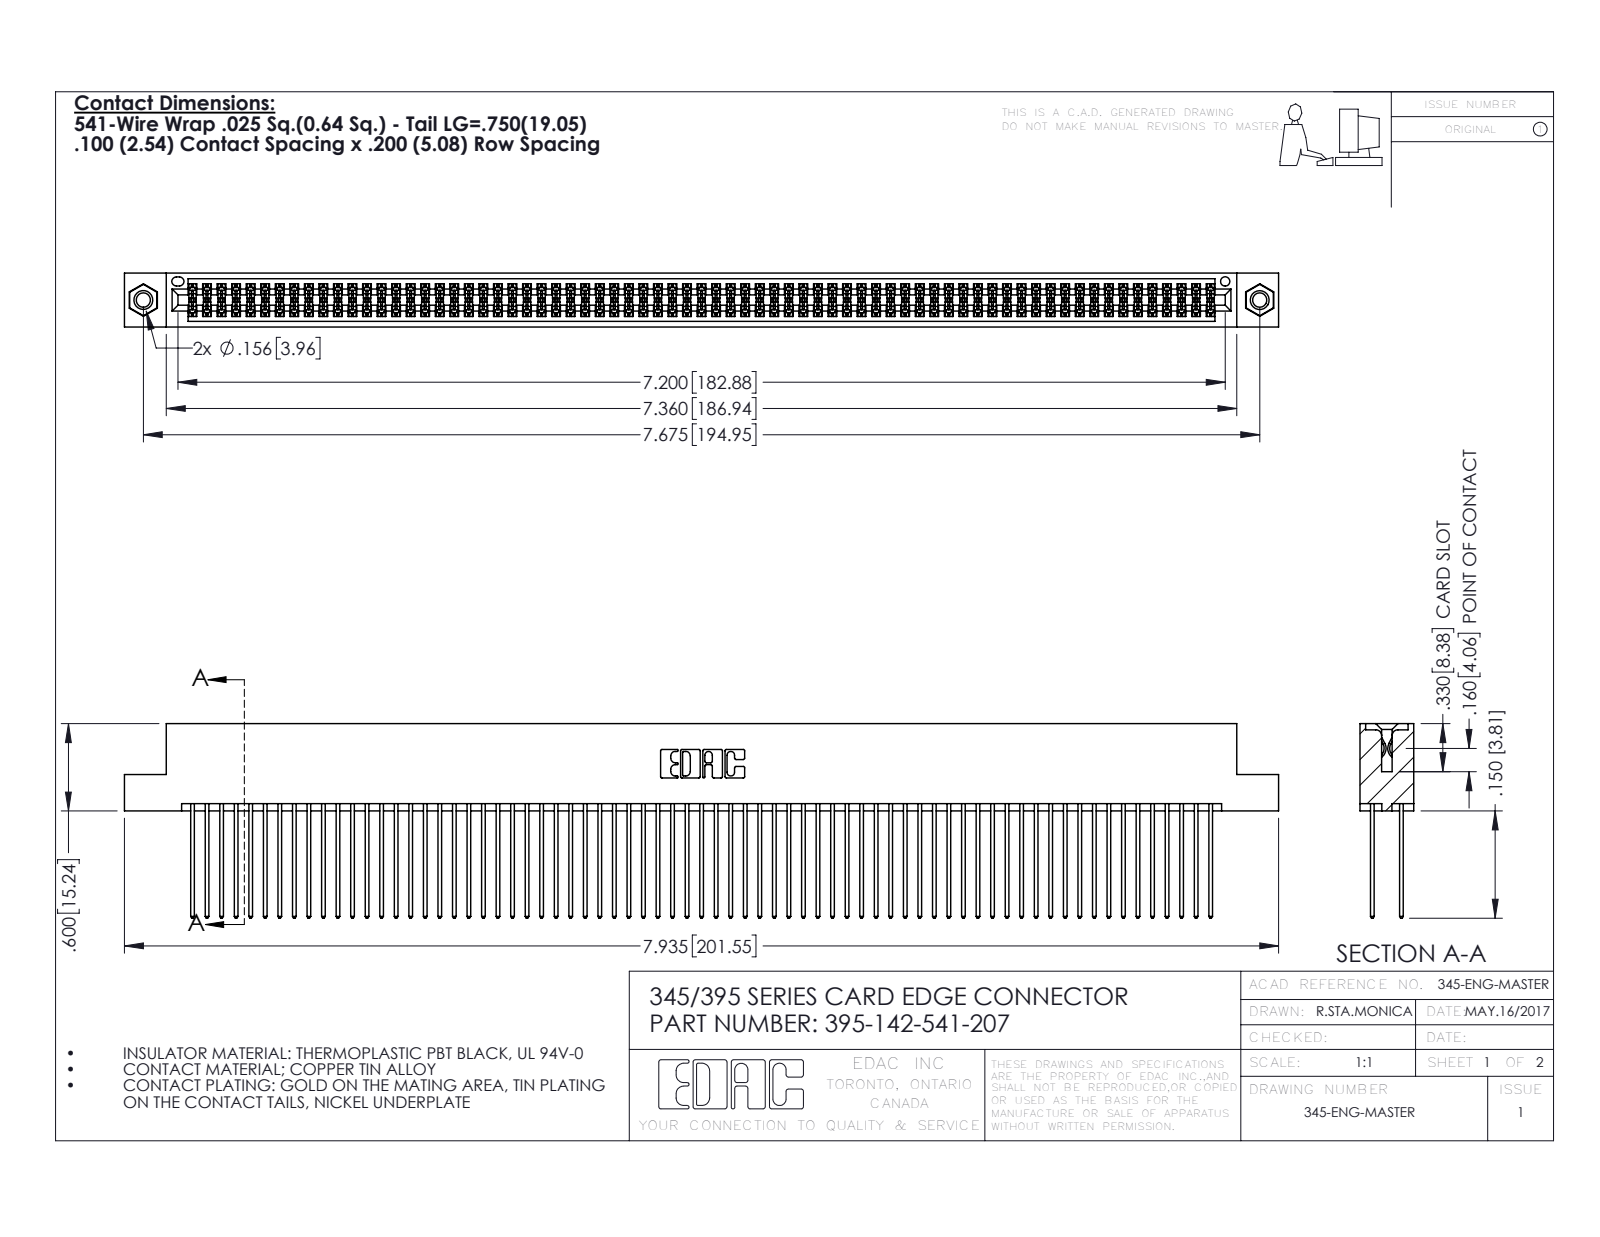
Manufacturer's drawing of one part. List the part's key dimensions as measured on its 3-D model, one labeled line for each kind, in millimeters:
Part name (STEP PRODUCT): 345 Part_Flush Mounting Lugs - 0.156 Dia-TI; 395-142-541-207; 345-292-001_345-293-141; 345-250-001_345-250-005-103
STEP written by: SolidWorks 2016 (CONFIG_CONTROL_DESIGN)
Units: millimetres
Bodies: 145 solids, 7286 faces (4798 planar, 2472 cylindrical, 16 other)
Overall size (bounding box): 201.5 × 34 × 9.4
Volume: 20 650 mm³ · Surface area: 34 940 mm²
Round holes (diameter × count): ⌀2.5 ×2, ⌀3.2 ×2, ⌀4 ×2, ⌀1.6 ×1
Round bosses / shafts (diameter × count): ⌀3.9 ×2
Partial cylindrical surfaces — rounded edges, fillets, slot ends (radius × count): R0.2 ×213, R0.3 ×142, R0.3 ×22, R0.2 ×6, R0.8 ×6, R0.7 ×3, R0.4 ×2, R0.5 ×2
Main face-to-face distances: 1.8, 7.6, 5.1, 2.5, 6.9, 0.6, 5.7, 9.4, 4.4, 3.8
Hole centre spacings: 6.9, 189, 194.9
